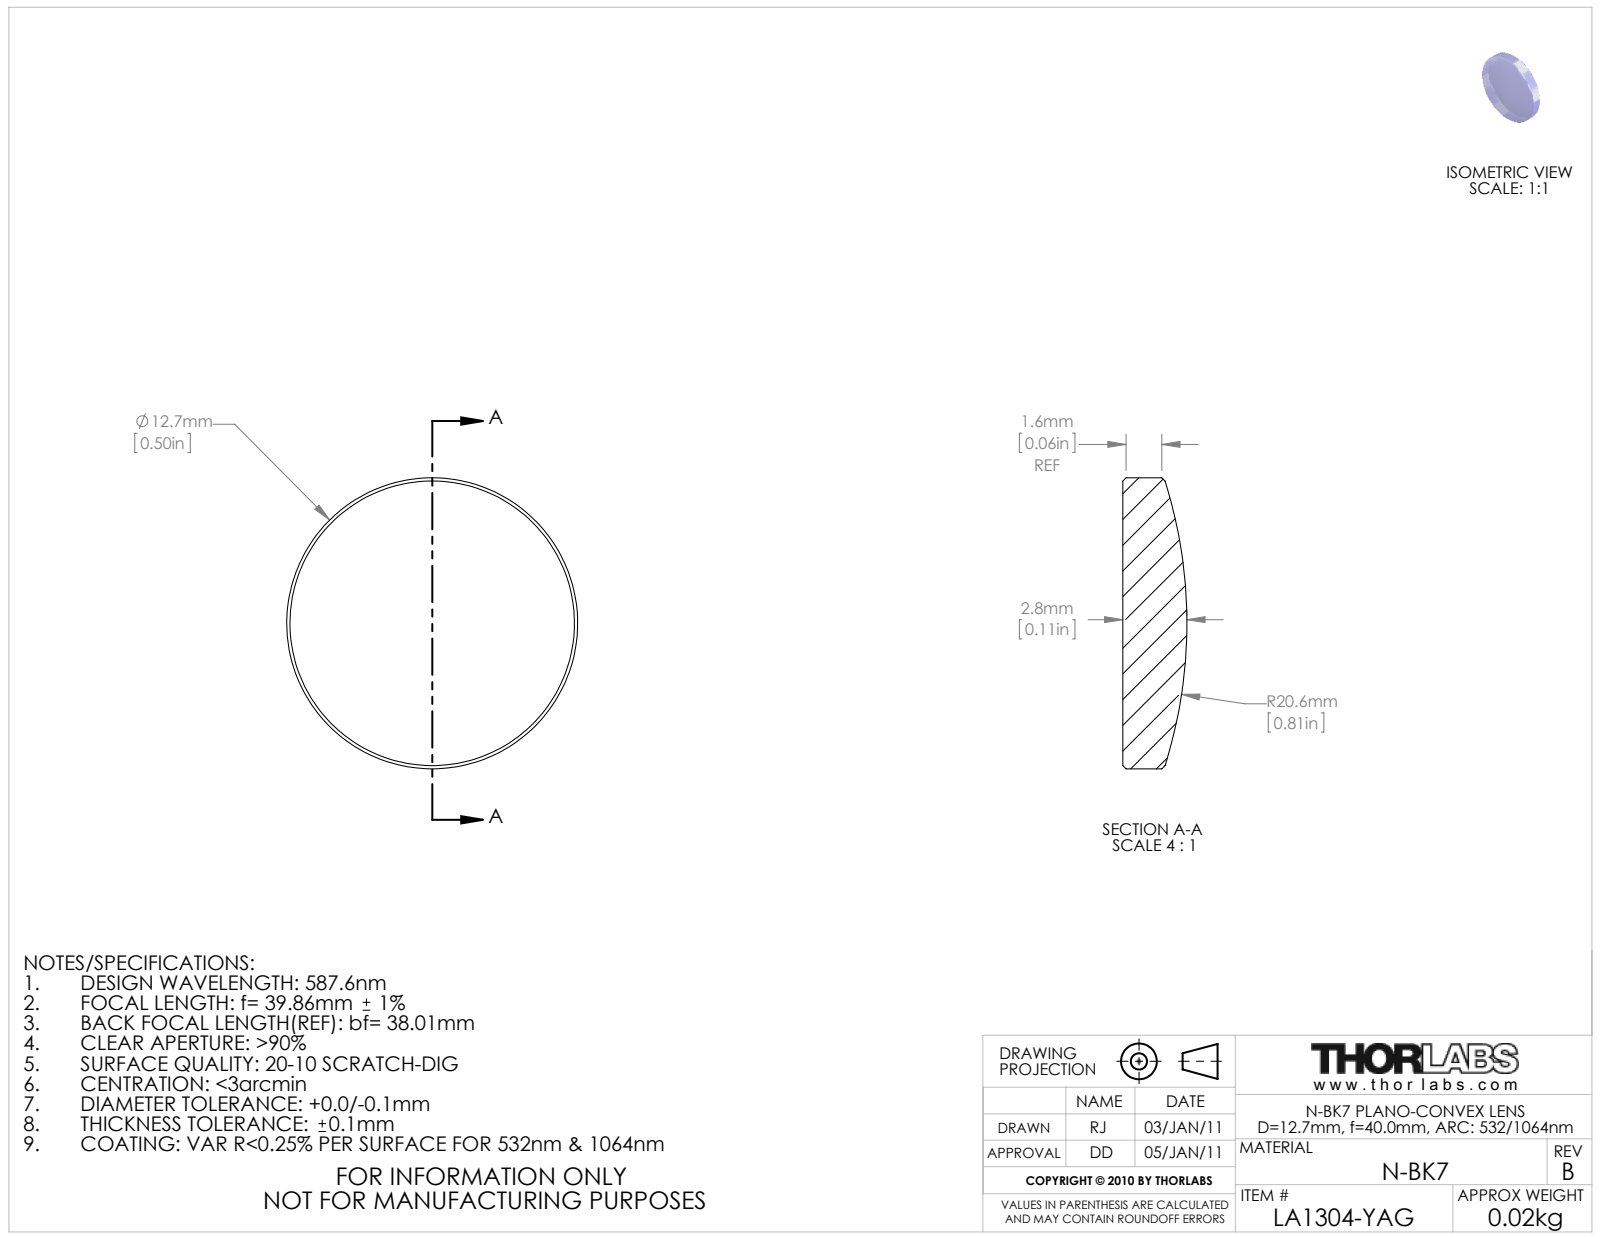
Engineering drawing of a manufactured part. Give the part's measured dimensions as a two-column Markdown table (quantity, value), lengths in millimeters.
| quantity | value |
| --- | --- |
| part name | 21779-E0W |
| STEP written by | SolidWorks 2011 (AUTOMOTIVE_DESIGN) |
| units | millimeters |
| bodies | 0 solids, 9 faces (1 planar, 2 cylindrical, 6 other) |
| overall size | 12.7 × 12.7 × 2.8 |
| round bosses / shafts (diameter × count) | 12.7 × 1 |
